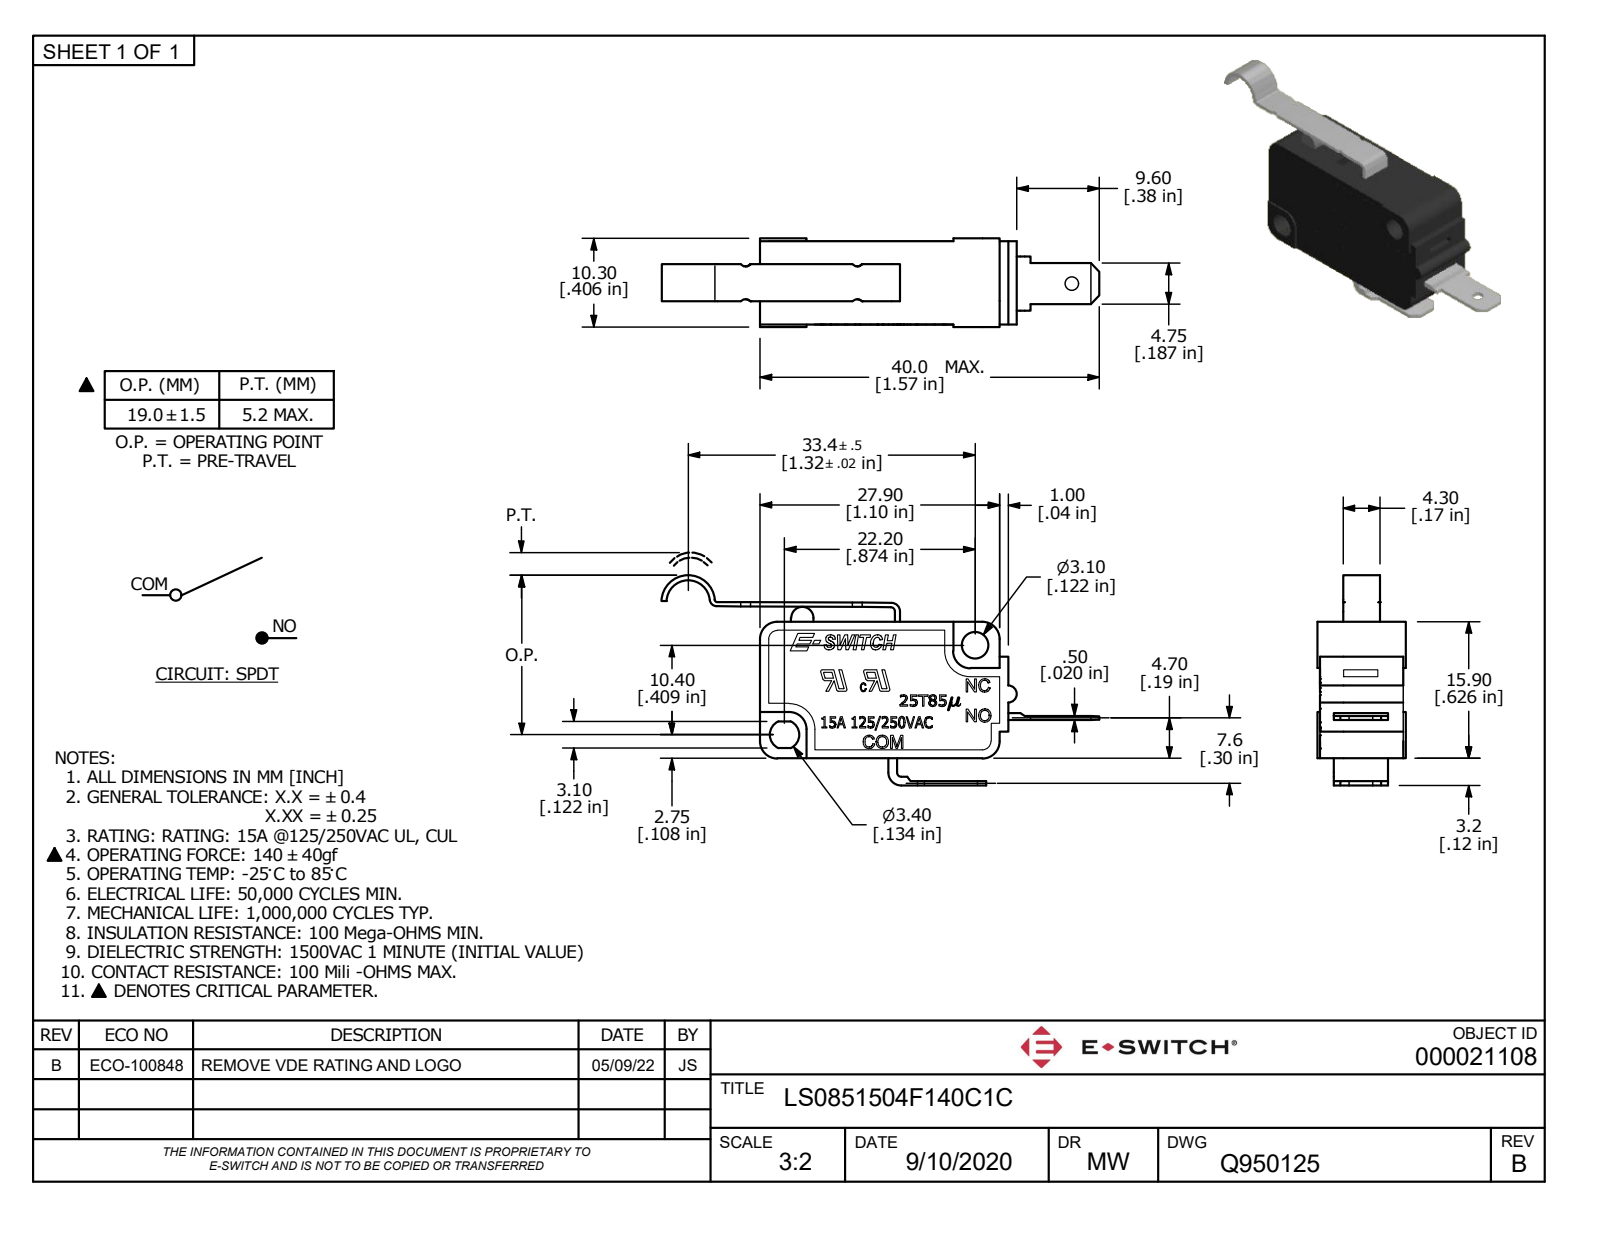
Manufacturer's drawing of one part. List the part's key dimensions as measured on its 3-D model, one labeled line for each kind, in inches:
Part name (STEP PRODUCT): LS0851504F140C1C
STEP written by: Autodesk Inventor 2022 (AUTOMOTIVE_DESIGN)
Units: inches
Bodies: 1 solid, 783 faces (510 planar, 66 cylindrical, 207 other)
Overall size (bounding box): 2.006 × 0.963 × 0.406
Volume: 0.267 in³ · Surface area: 4.168 in²
Round holes (diameter × count): ⌀0.063 ×2, ⌀0.122 ×1
Partial cylindrical surfaces — rounded edges, fillets, slot ends (radius × count): R0.008 ×8, R0.079 ×6, R0.03 ×4, R0.039 ×4, R0.018 ×3, R0.026 ×3, R0.02 ×2, R0.118 ×2
Main face-to-face distances: 0.383, 0.626, 0.382, 0.02, 0.382, 0.394, 0.394, 1.138, 0.319, 0.039
Hole centre spacings: 0.533
